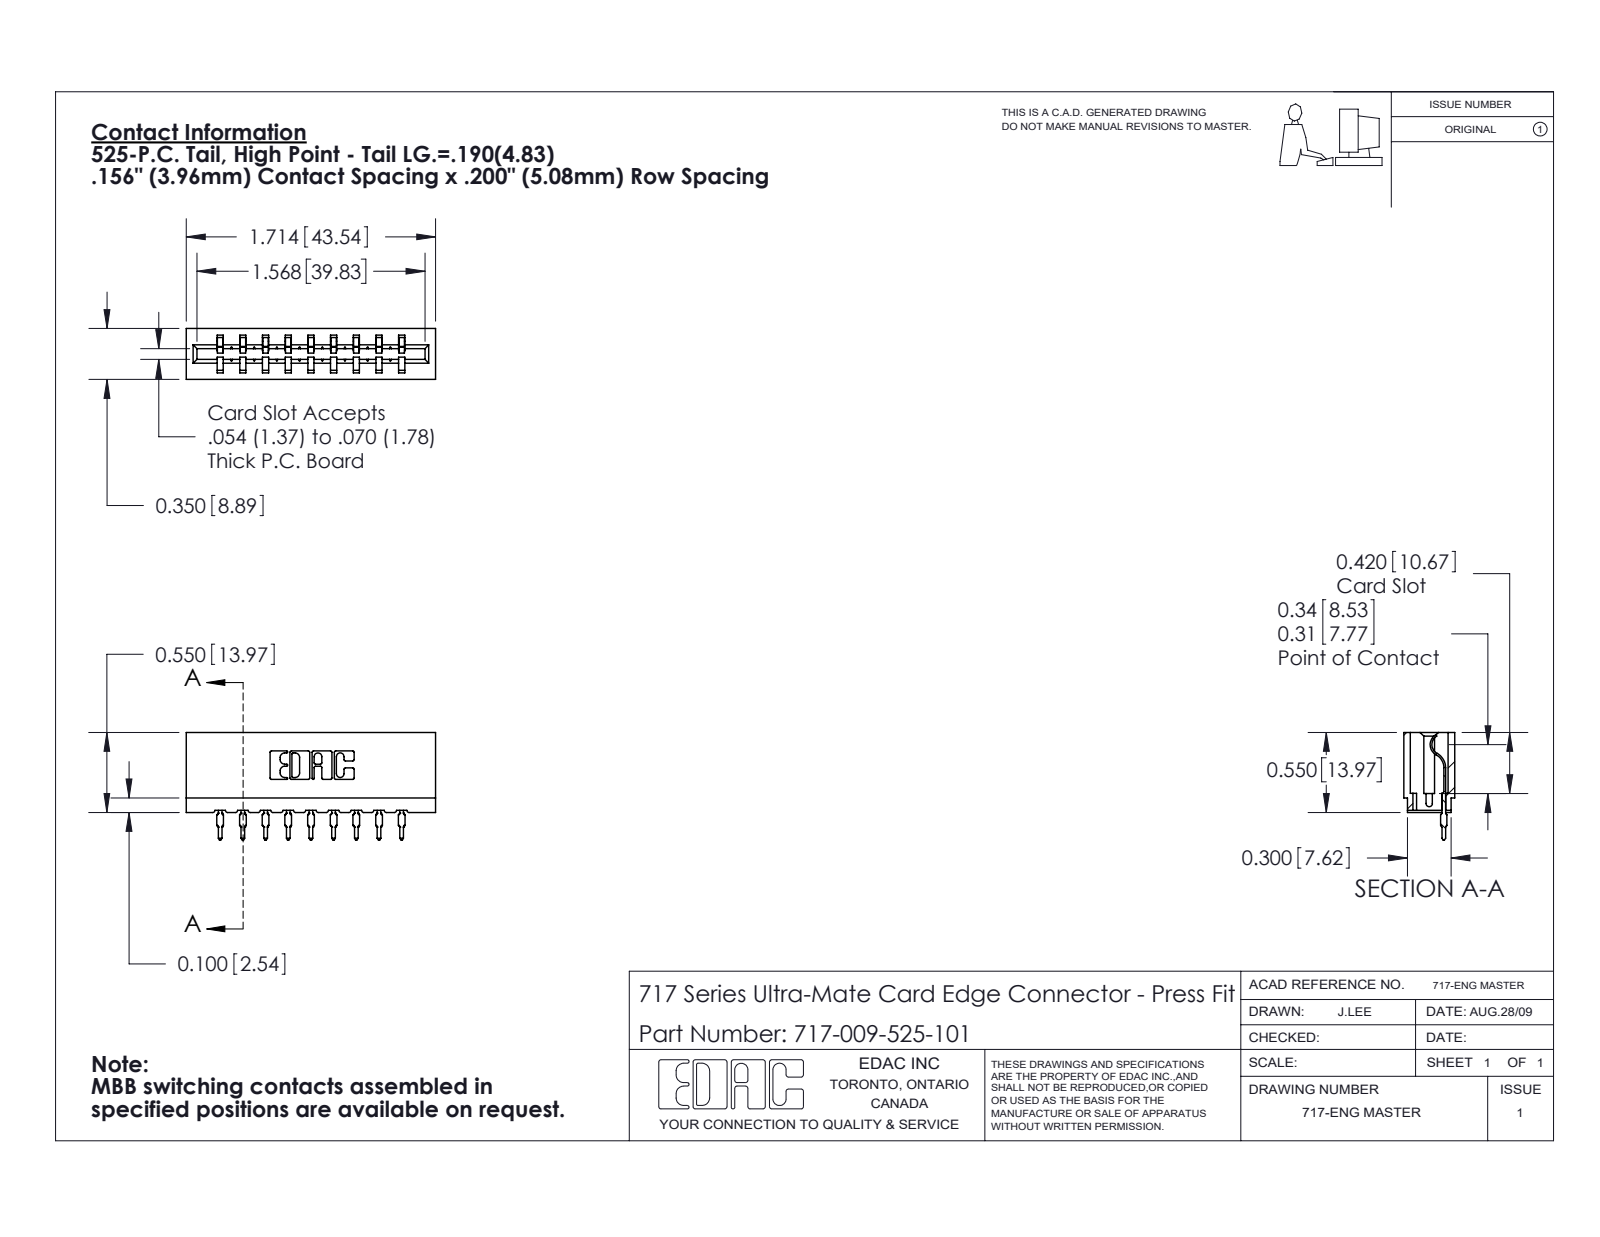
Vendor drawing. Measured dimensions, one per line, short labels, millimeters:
name: 745-292-001_525; 717 Part_Insulator Option - 06; 717-009-525-101
written by: SolidWorks 2020 (CONFIG_CONTROL_DESIGN)
unit: mm
bodies: 10 solids, 1111 faces (666 planar, 211 cylindrical, 234 other)
size: 43.5 × 18.8 × 8.9
volume: 3 820 mm³; area: 4 977 mm²
rounds: 22× R0.3, 18× R0.4, 18× R0.5, 6× R0.2, 6× R0.8, 4× R0.1, 4× R0.3, 3× R0.7
face distances: 4, 5.4, 15.8, 3.5, 11.9, 5, 8.9, 7.9, 1.1, 7.9
